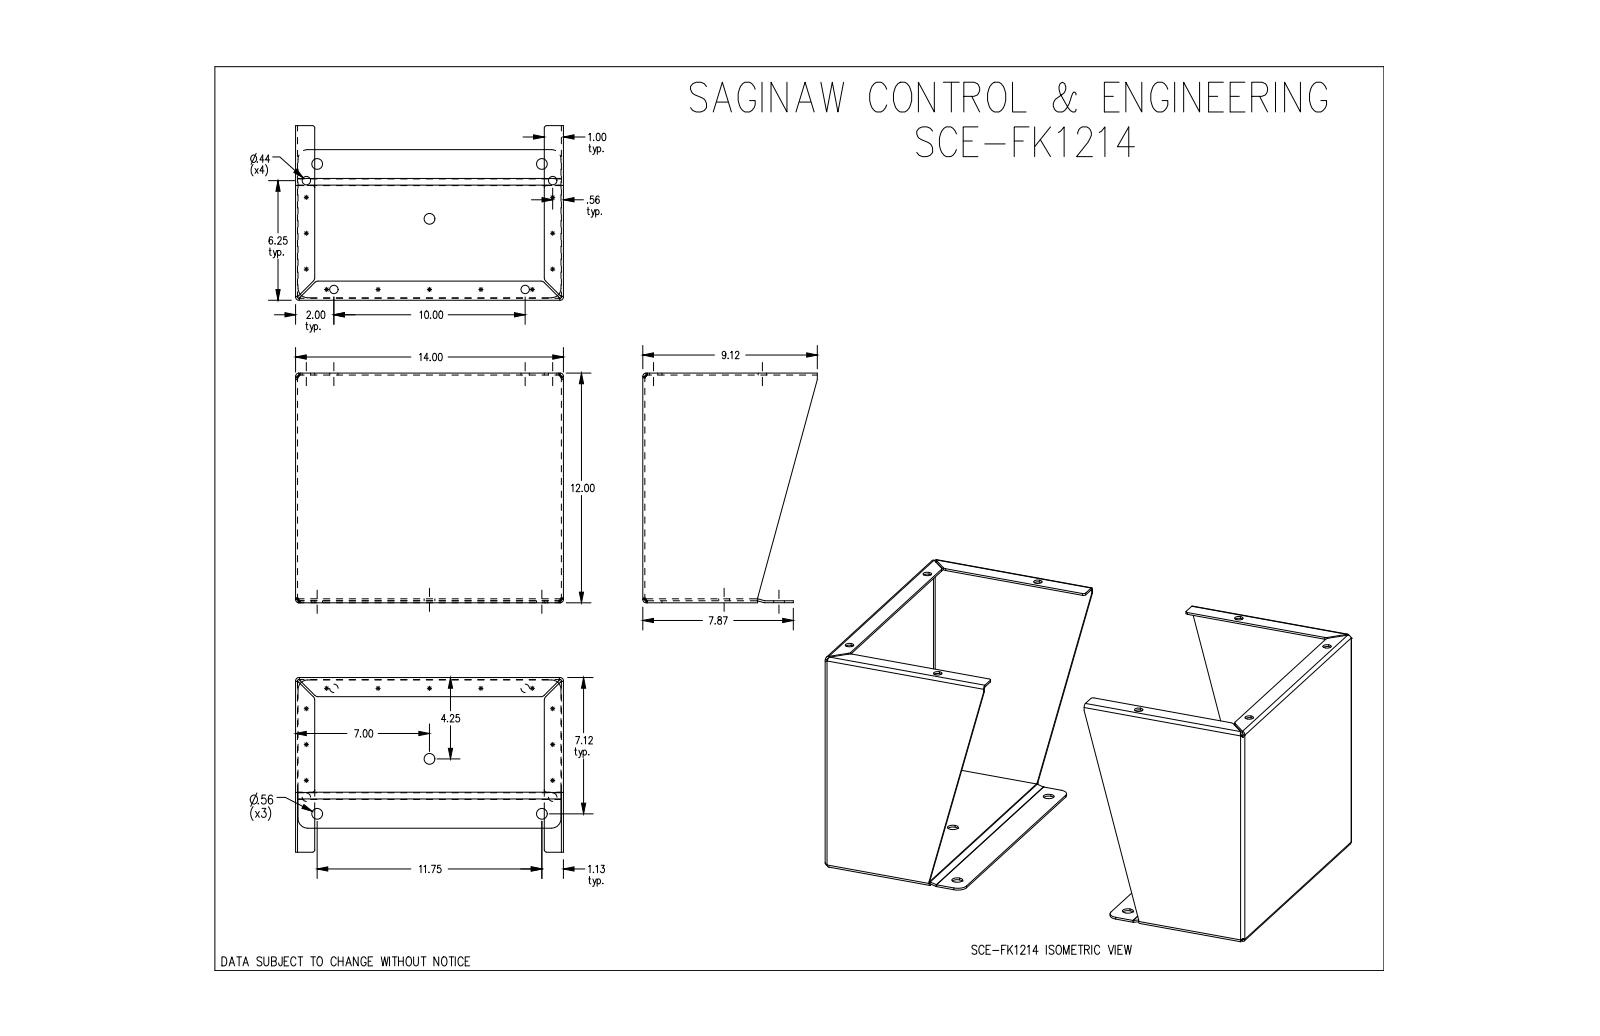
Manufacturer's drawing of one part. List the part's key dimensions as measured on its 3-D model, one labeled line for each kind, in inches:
Part name (STEP PRODUCT): SCE-FK1214
STEP written by: SolidWorks 2019 (CONFIG_CONTROL_DESIGN)
Units: inches
Bodies: 4 solids, 214 faces (96 planar, 86 cylindrical, 32 other)
Overall size (bounding box): 24 × 14 × 12
Volume: 103.1 in³ · Surface area: 2 013 in²
Round holes (diameter × count): ⌀0.437 ×8, ⌀0.563 ×6
Partial cylindrical surfaces — rounded edges, fillets, slot ends (radius × count): R0.166 ×16, R0.062 ×10, R0.125 ×8, R0.22 ×8, R0.5 ×8, R0.063 ×6
Main face-to-face distances: 0.104, 13.896, 23.896, 13.792, 14, 24, 23.792, 11.792, 11.896, 0.101
Hole centre spacings: 1.035, 5.866, 6.213, 6.614, 6.741, 10.646, 12.774, 13.93
